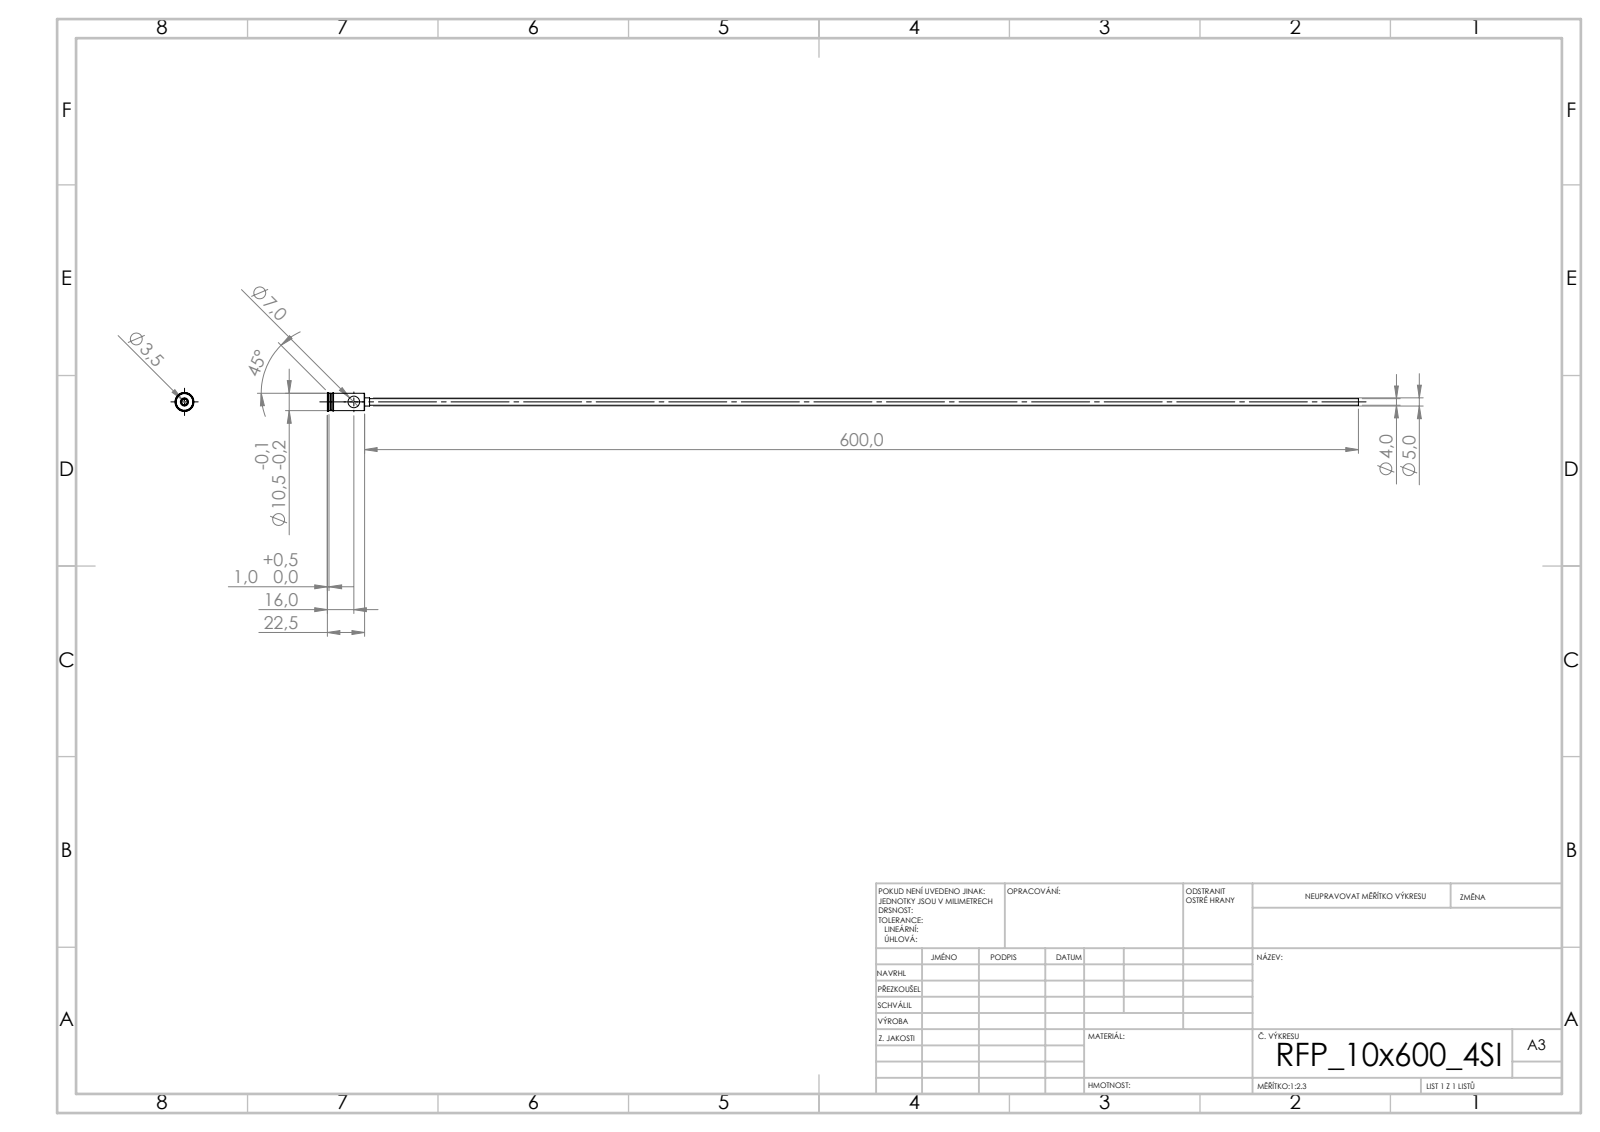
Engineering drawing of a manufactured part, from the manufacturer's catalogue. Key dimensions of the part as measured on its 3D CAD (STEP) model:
STEP written by: SolidWorks 2019 (CONFIG_CONTROL_DESIGN)
Units: millimetres
Bodies: 1 solid, 44 faces (20 planar, 16 cylindrical, 8 other)
Overall size (bounding box): 622.5 × 11.5 × 11.5
Volume: 3 281 mm³ · Surface area: 15 287 mm²
Round holes (diameter × count): ⌀3.5 ×1, ⌀7 ×1
Round bosses / shafts (diameter × count): ⌀11.5 ×1, ⌀10.5 ×1, ⌀5 ×1, ⌀4 ×1
Main face-to-face distances: 22.5, 20.5, 2, 5.9, 20.2, 2.3, 3, 23.2, 23.5, 25.5
